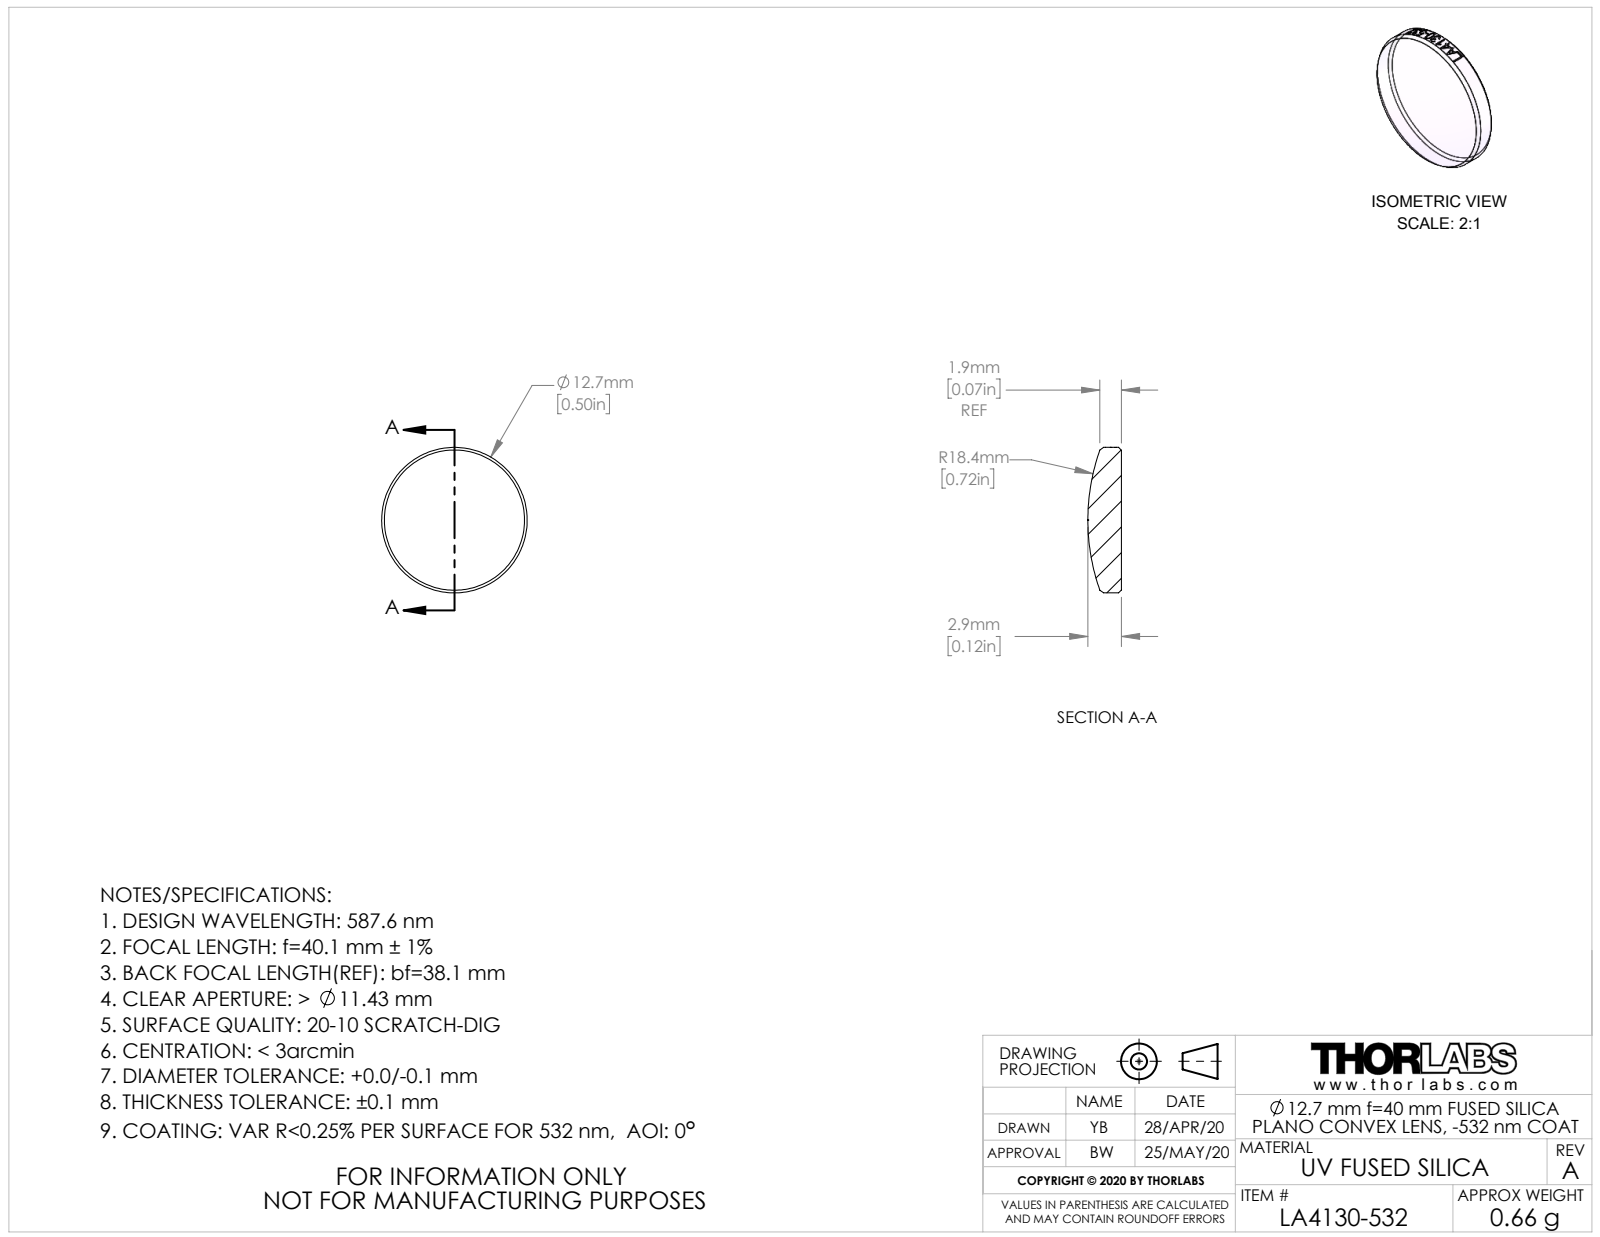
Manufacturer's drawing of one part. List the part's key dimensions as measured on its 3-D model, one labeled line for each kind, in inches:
Part name (STEP PRODUCT): CTN015735-E0W
STEP written by: SolidWorks 2018 (AUTOMOTIVE_DESIGN)
Units: inches
Bodies: 1 solid, 28 faces (1 planar, 21 cylindrical, 6 other)
Overall size (bounding box): 0.5 × 0.5 × 0.115
Volume: 0.018 in³ · Surface area: 0.496 in²
Round bosses / shafts (diameter × count): ⌀0.5 ×1
